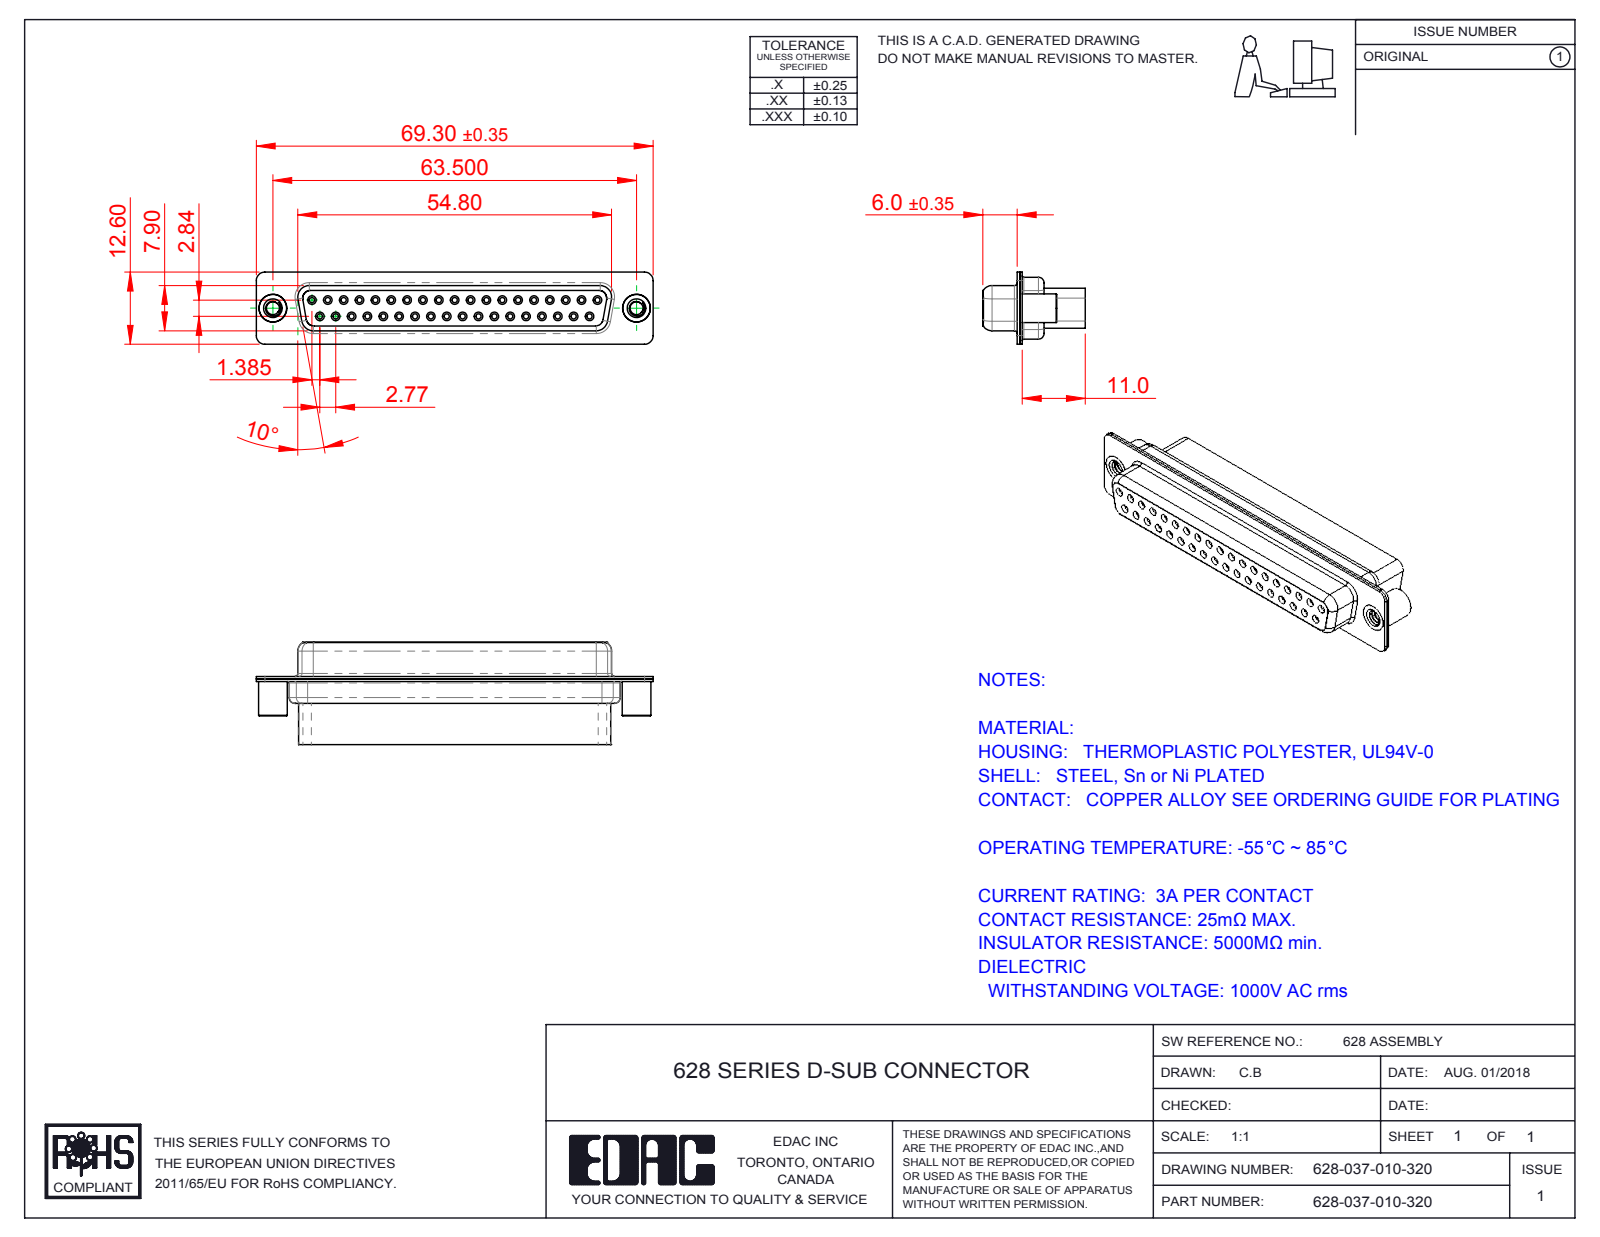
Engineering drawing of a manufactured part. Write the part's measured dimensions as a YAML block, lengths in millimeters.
part_name: "628 Shell Rear_37 Contacts; 628 Shell Front_37 Contacts; 628 4-40 Threaded Standoff BS; 628 Housing_37 HP (+1 more)"
step_written_by: "SolidWorks 2016 (CONFIG_CONTROL_DESIGN)"
units: millimeters
bodies: {solids: 5, faces: 782, planar: 178, cylindrical: 453, other: 151}
overall_size: [69.3, 17.9, 12.6]
volume: 6761
surface_area: 11144
round_holes:
  - {diameter: 0.9, count: 37}
  - {diameter: 1.5, count: 37}
  - {diameter: 2, count: 37}
  - {diameter: 1.7, count: 19}
  - {diameter: 1.6, count: 18}
  - {diameter: 2.26, count: 2}
  - {diameter: 4, count: 2}
  - {diameter: 4.05, count: 2}
  - {diameter: 4.85, count: 2}
round_bosses_or_shafts:
  - {diameter: 5, count: 2}
  - {diameter: 4.95, count: 2}
  - {diameter: 4.8, count: 2}
partial_cylinders:
  - {radius: 1.5, count: 16}
  - {radius: 2, count: 12}
  - {radius: 0.25, count: 4}
  - {radius: 0.5, count: 4}
  - {radius: 0.6, count: 4}
  - {radius: 0.65, count: 4}
  - {radius: 0.95, count: 4}
  - {radius: 1, count: 4}
face_to_face_distances: [0.4, 0.45, 6.6, 7, 1.9, 8.5, 0.85, 7.05, 7.45, 1.4]
hole_center_spacings: [3.16, 2.77, 5.54, 8.31, 5.04, 7.49, 11.08, 13.85]
